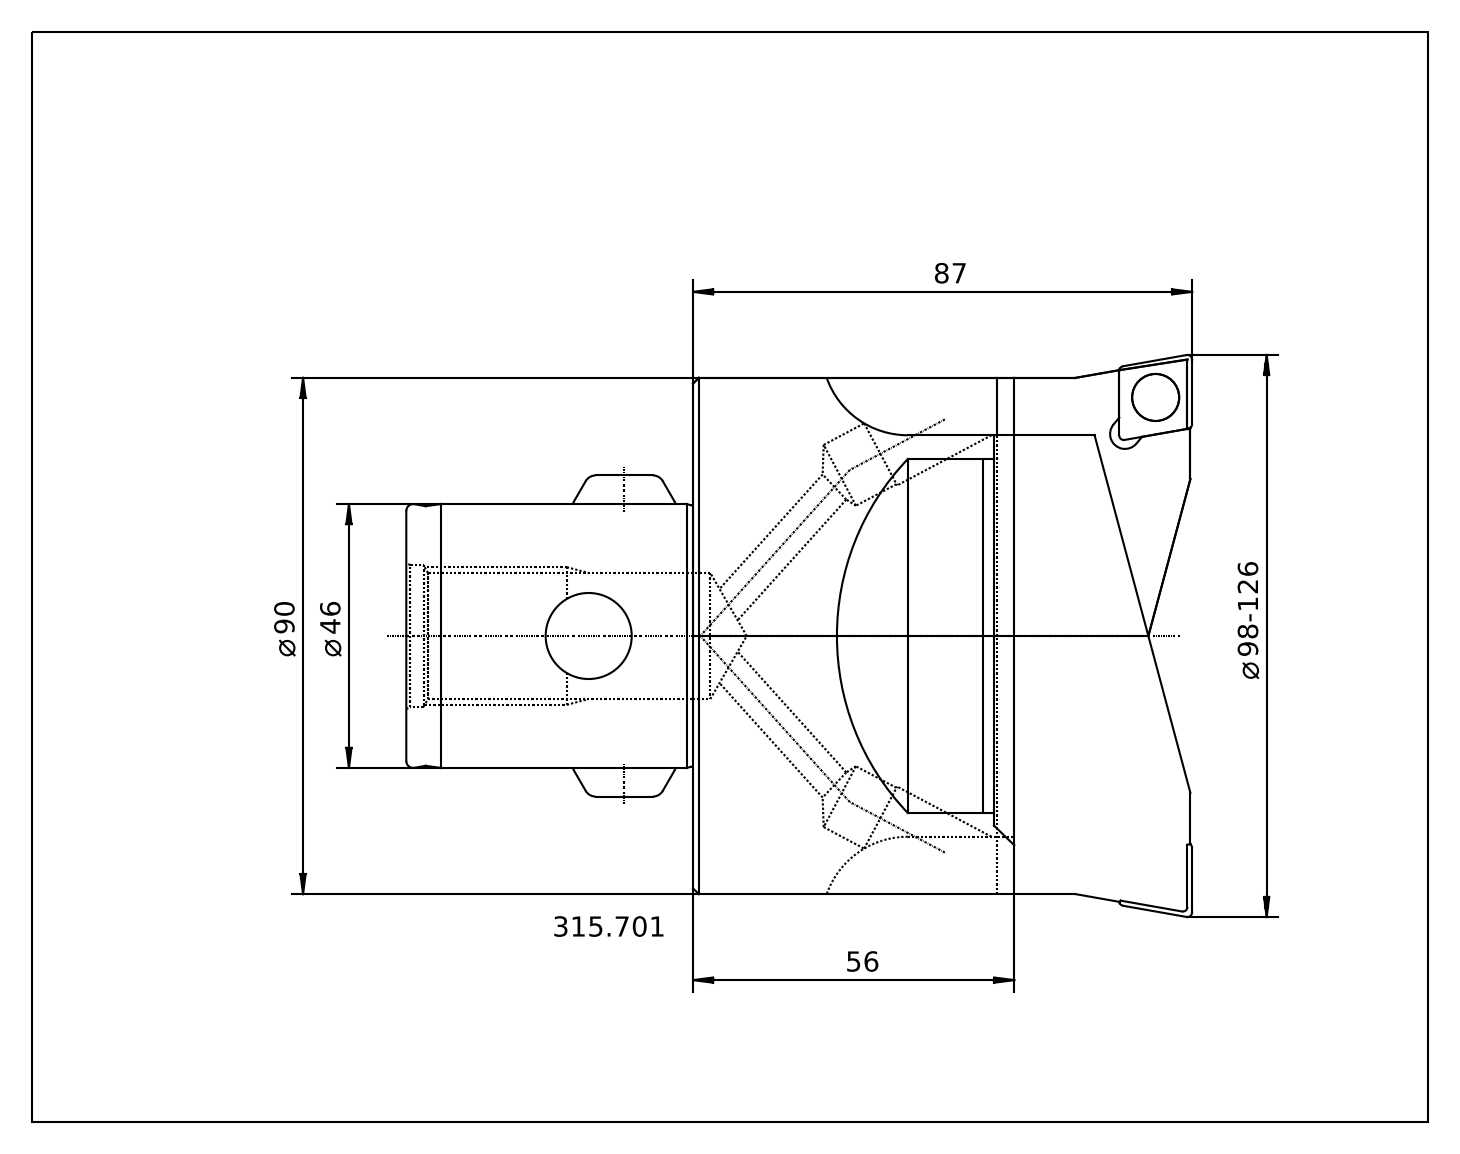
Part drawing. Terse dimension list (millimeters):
name: 315.701 Kaiser TWN 98-153 X CK7|315.750 Kaiser ETL M12_12.15 X 44_Standard;NONE; 315.701 Kaiser TWN 98-153 X CK7|691.507 Kaiser ETL �18 X 56K_Standard|693.306 Sprengring_Standard;NONE; 315.701 Kaiser TWN 98-153 X CK7|691.507 Kaiser ETL �18 X 56K_Standard|691.527 Mitnehmerbolzen_Standard;NONE; 315.701 Kaiser TWN 98-153 X CK7|315.730 Kaiser TW 98-153 X CK7B_Standard|315.730 Kaiser TW 98-153 X CK7B_Standard;NONE
written by: ACIS (automotive_design)
unit: mm
bodies: 15 solids, 456 faces (91 planar, 131 cylindrical, 234 other)
size: 146 × 90 × 90
volume: 389 402 mm³; area: 68 540 mm²
holes: 6× ⌀12, 4× ⌀10, 4× ⌀10.2, 2× ⌀4.3, 2× ⌀6, 2× ⌀7.8, 2× ⌀12.2, 2× ⌀12.5, 1× ⌀15, 1× ⌀22.1, 1× ⌀24, 1× ⌀24.7
bosses: 4× ⌀20, 4× ⌀12.15, 4× ⌀11.65, 4× ⌀9.4, 2× ⌀11.7, 1× ⌀90, 1× ⌀46, 1× ⌀18
rounds: 2× R15
face distances: 56, 32.5, 3, 53, 103, 106, 50, 70, 30, 40
hole spacings: 16.12, 21.26, 24, 29.12, 32.25, 42.52
